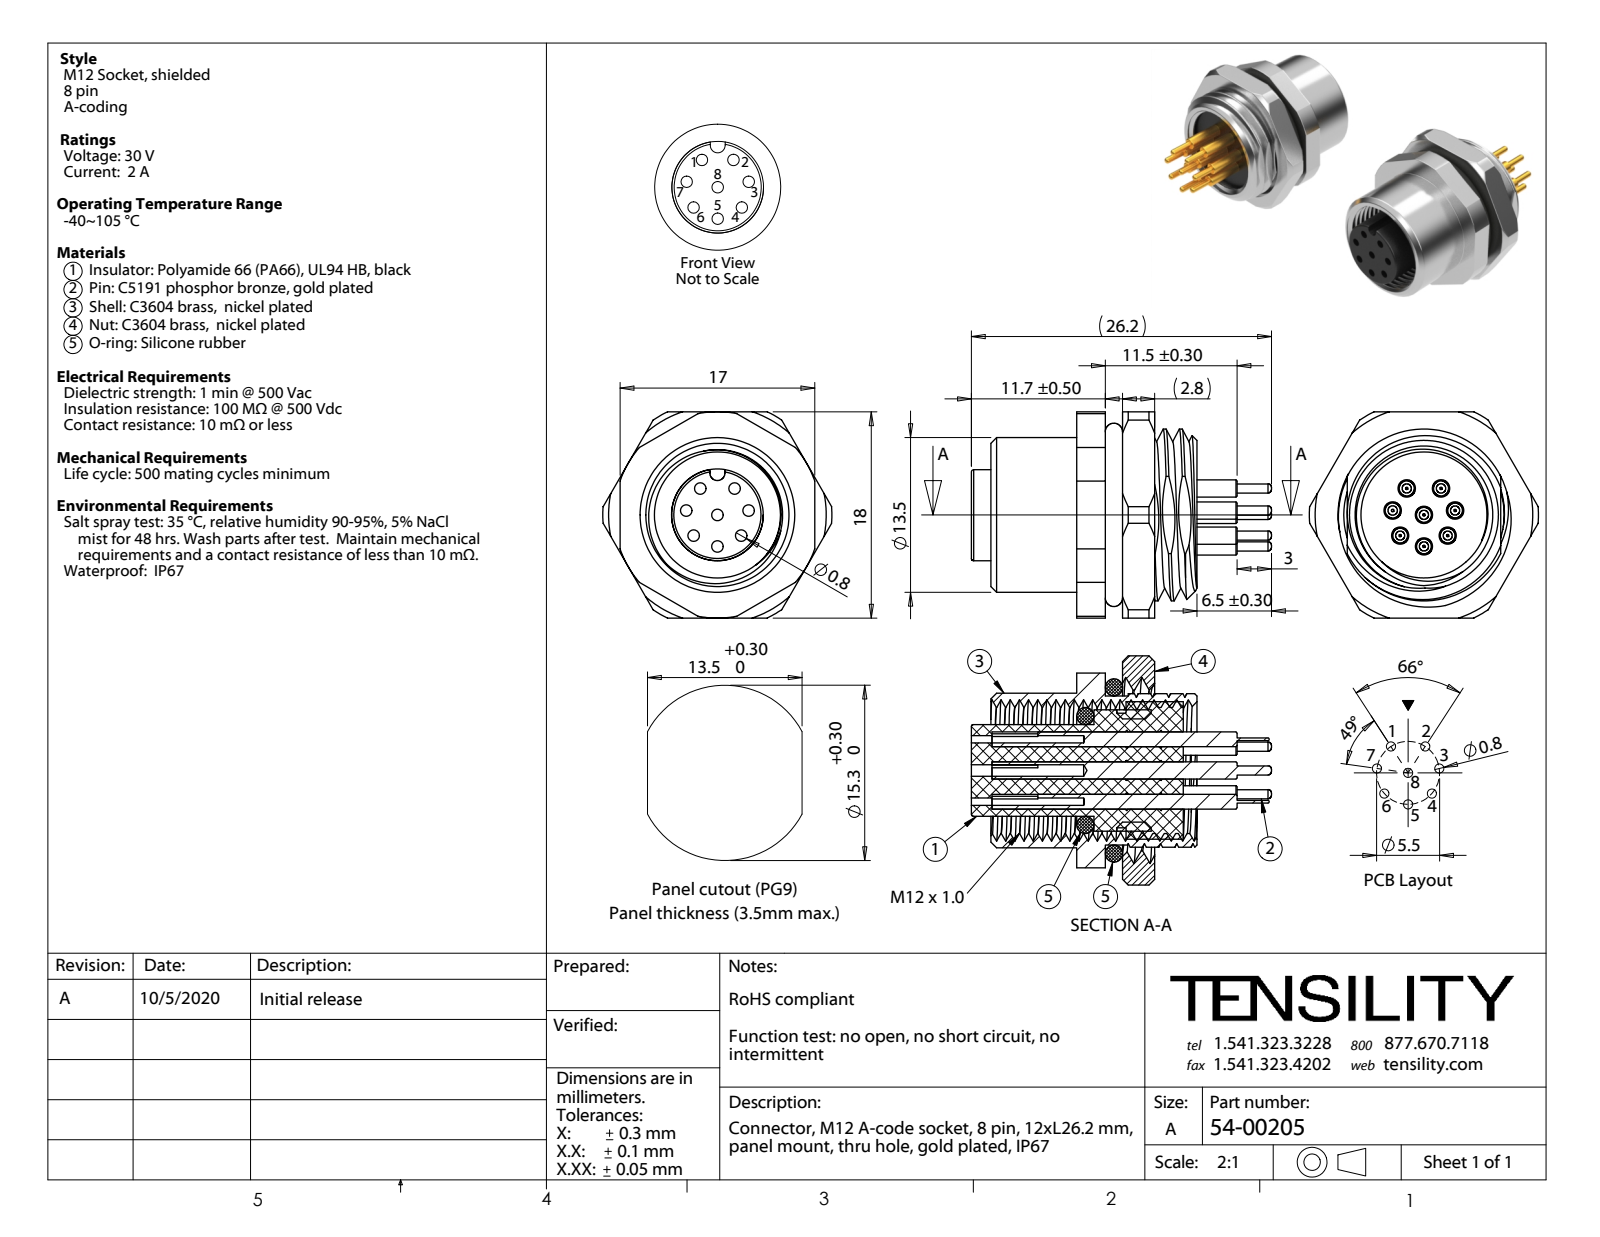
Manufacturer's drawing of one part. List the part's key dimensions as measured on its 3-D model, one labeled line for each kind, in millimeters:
Part name (STEP PRODUCT): 54-00205-01; 54-00205-05; 54-00205; 54-00205-02 (+3 more)
STEP written by: SolidWorks 2021 (CONFIG_CONTROL_DESIGN)
Units: millimetres
Bodies: 13 solids, 480 faces (145 planar, 202 cylindrical, 133 other)
Overall size (bounding box): 26.2 × 20 × 18
Volume: 2 752 mm³ · Surface area: 6 298 mm²
Round holes (diameter × count): ⌀1 ×8, ⌀11 ×1, ⌀14 ×1
Round bosses / shafts (diameter × count): ⌀1.5 ×8, ⌀0.8 ×8, ⌀13.5 ×1, ⌀13 ×1, ⌀12 ×1, ⌀10.6 ×1, ⌀9 ×1, ⌀8 ×1
Partial cylindrical surfaces — rounded edges, fillets, slot ends (radius × count): R0.6 ×4, R0.65 ×1, R7.5 ×1, R9 ×1, R10 ×1
Main face-to-face distances: 2.5, 6.8, 4.3, 2.8, 1.5, 5.3, 4, 1, 9.3, 1.8
Hole centre spacings: 2.75, 4.15, 2.27, 2.28, 2.29, 4.64, 5.27, 5.28
